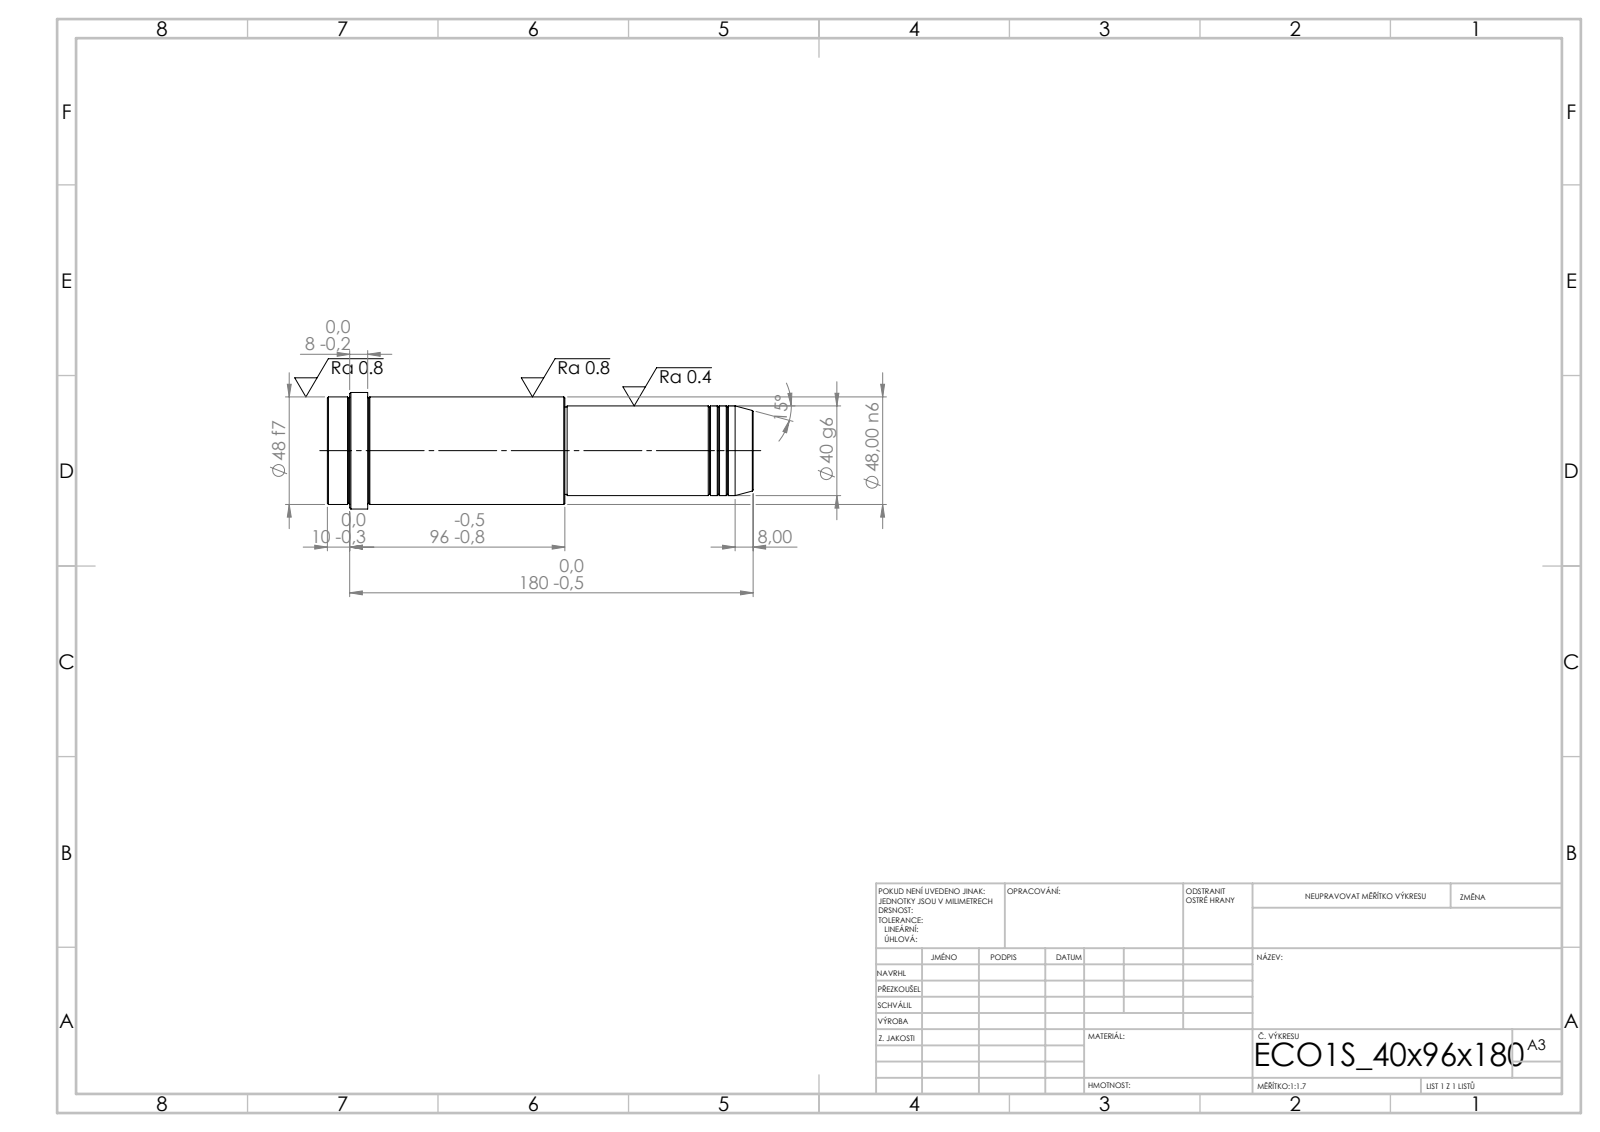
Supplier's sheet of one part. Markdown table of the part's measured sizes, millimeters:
| quantity | value |
| --- | --- |
| STEP written by | SolidWorks 2019 (CONFIG_CONTROL_DESIGN) |
| units | millimeters |
| bodies | 1 solid, 52 faces (6 planar, 16 cylindrical, 30 other) |
| overall size | 190 × 52 × 52 |
| volume | 298 458 mm³ |
| surface area | 30 956 mm² |
| round bosses / shafts (diameter × count) | 52 × 1, 48 × 1, 40 × 1, 39 × 1 |
| main face-to-face distances | 190, 84, 106, 172, 88, 18, 180, 96, 8, 10 |
